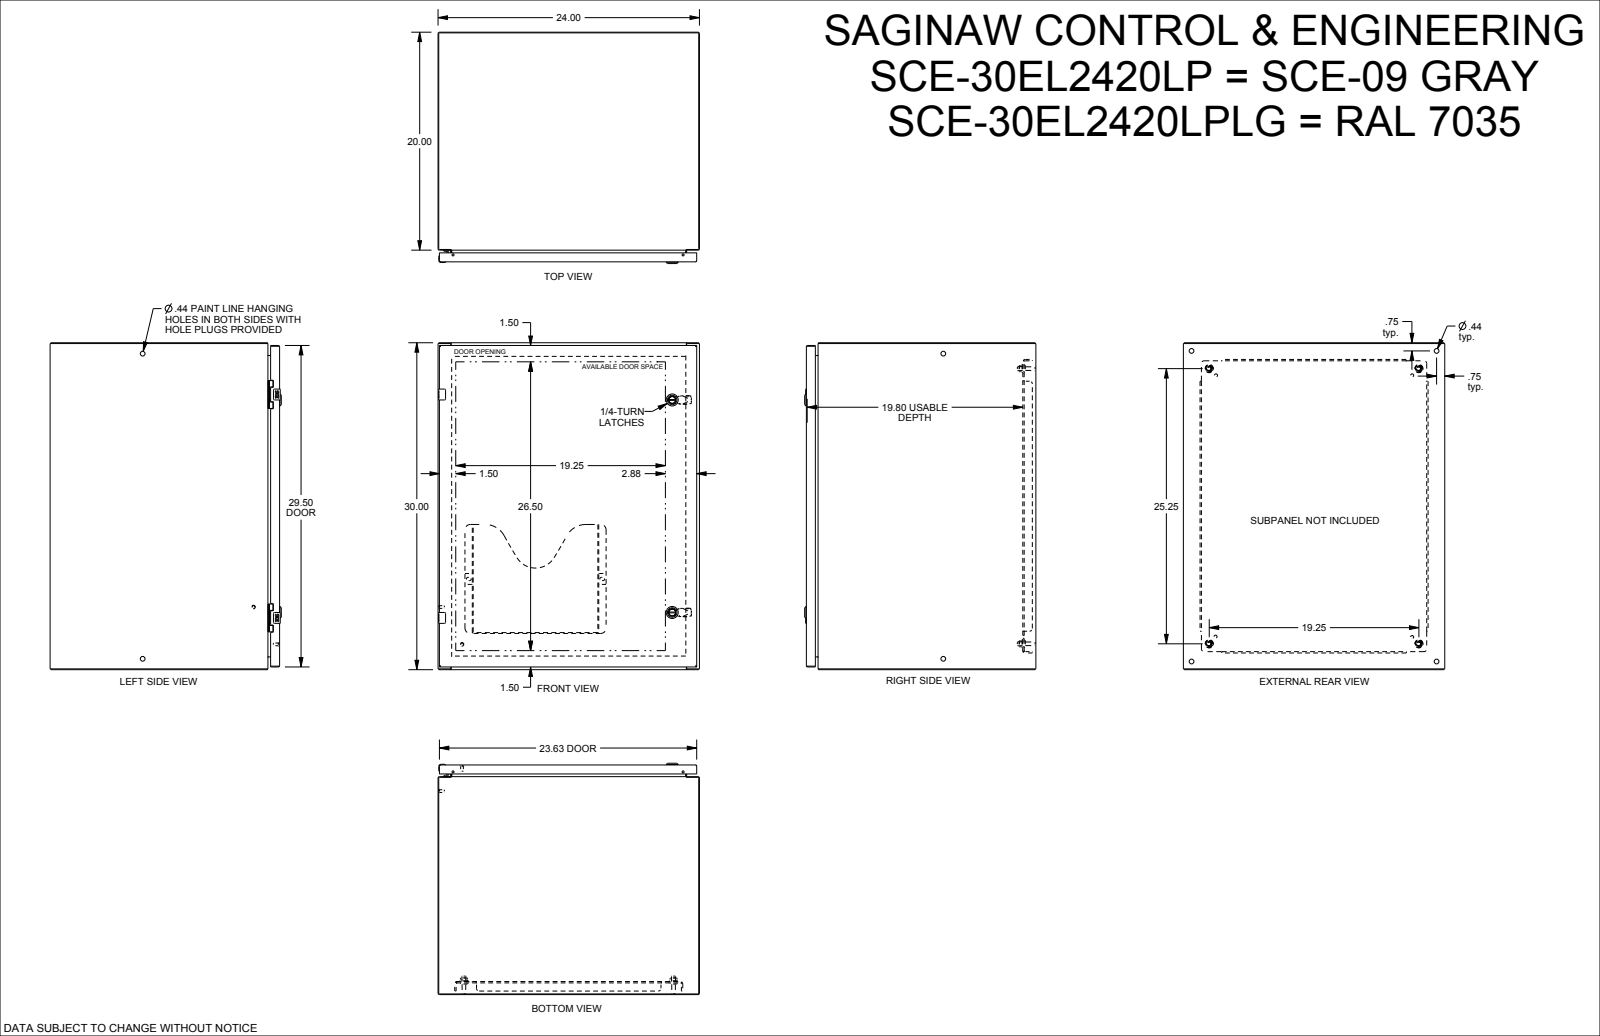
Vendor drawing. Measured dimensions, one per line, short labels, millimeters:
name: SCE-30EL2420LP
written by: SolidWorks 2021 (AUTOMOTIVE_DESIGN)
unit: mm
bodies: 47 solids, 2851 faces (1115 planar, 866 cylindrical, 870 other)
size: 762 × 609.6 × 539.2
volume: 6 289 000 mm³; area: 6 112 000 mm²
holes: 6× ⌀11.1, 4× ⌀4.4, 4× ⌀5.2, 4× ⌀6.2, 4× ⌀6.8, 4× ⌀7.1, 4× ⌀9.3, 4× ⌀9.5, 4× ⌀12.7, 2× ⌀1, 2× ⌀4.8, 2× ⌀5
bosses: 6× ⌀4.3, 4× ⌀9.3, 4× ⌀8.4, 4× ⌀6.4, 4× ⌀6.3, 4× ⌀6.1, 3× ⌀5, 2× ⌀28
rounds: 56× R0.3, 28× R0.3, 24× R0.4, 20× R0.5, 17× R1, 13× R1.5, 12× R0.7, 12× R2.5
face distances: 1.9, 607.7, 760.1, 1.5, 531.8, 535.3, 533.3, 533.7, 30.5, 504.8
hole spacings: 25, 520.7, 0.5, 12.5, 12.5, 22.2, 114.1, 531.8
